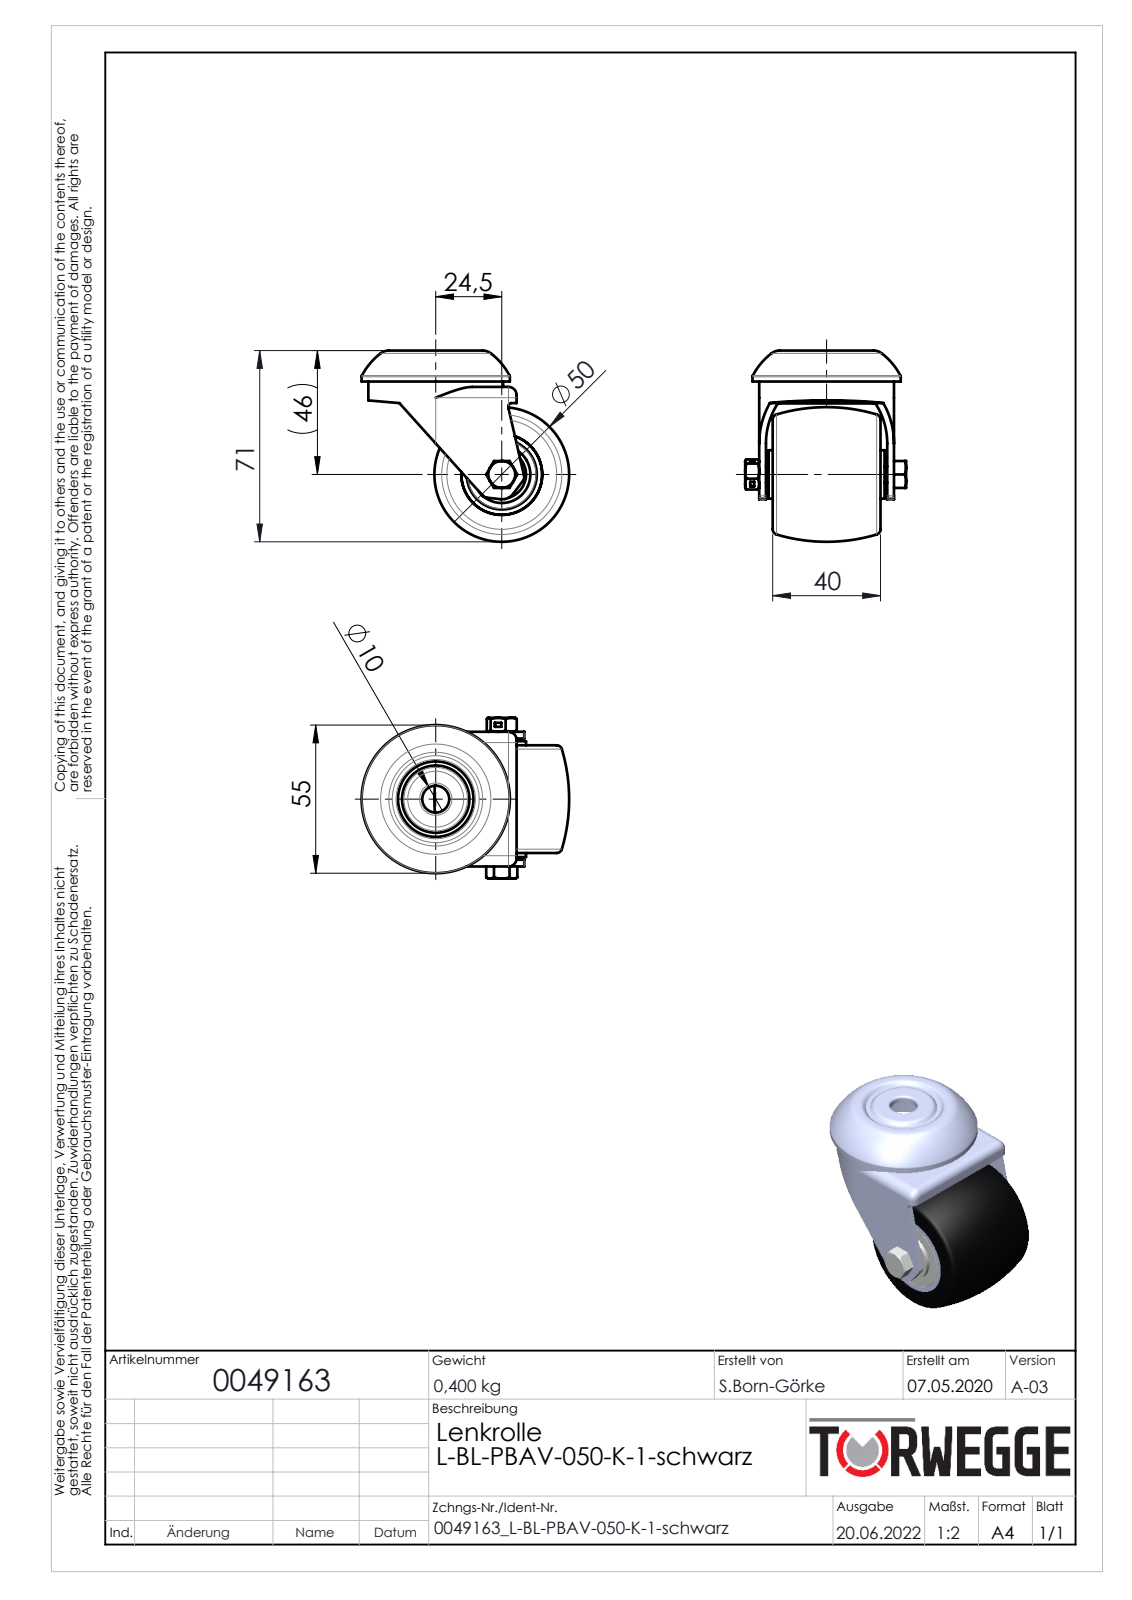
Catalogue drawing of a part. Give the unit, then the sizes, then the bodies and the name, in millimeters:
Units: millimetres
Overall size (bounding box): 77 × 71 × 59.7
Round holes (diameter × count): ⌀10 ×2, ⌀5 ×1, ⌀6 ×1, ⌀6.1 ×1, ⌀8 ×1, ⌀12.4 ×1, ⌀14.5 ×1, ⌀20 ×1, ⌀21.2 ×1, ⌀26 ×1, ⌀30 ×1, ⌀45 ×1
Round bosses / shafts (diameter × count): ⌀55 ×1, ⌀50 ×1, ⌀21.5 ×1, ⌀18 ×1, ⌀15 ×1, ⌀14.8 ×1, ⌀9.95 ×1, ⌀7.9 ×1
Partial cylindrical surfaces — rounded edges, fillets, slot ends (radius × count): R0.5 ×3, R3 ×3, R1.5 ×2, R2 ×2, R4 ×2, R1 ×1, R5 ×1
Main face-to-face distances: 2.5, 45, 5, 32, 47.5, 42.5, 40, 8, 10.5, 13
Volume: 83 982 mm³ · Surface area: 47 565 mm²
Bodies: 14 solids, 390 faces (89 planar, 105 cylindrical, 196 other)
Part name (STEP PRODUCT): 0049163
STEP written by: SolidWorks 2020 (AUTOMOTIVE_DESIGN)
